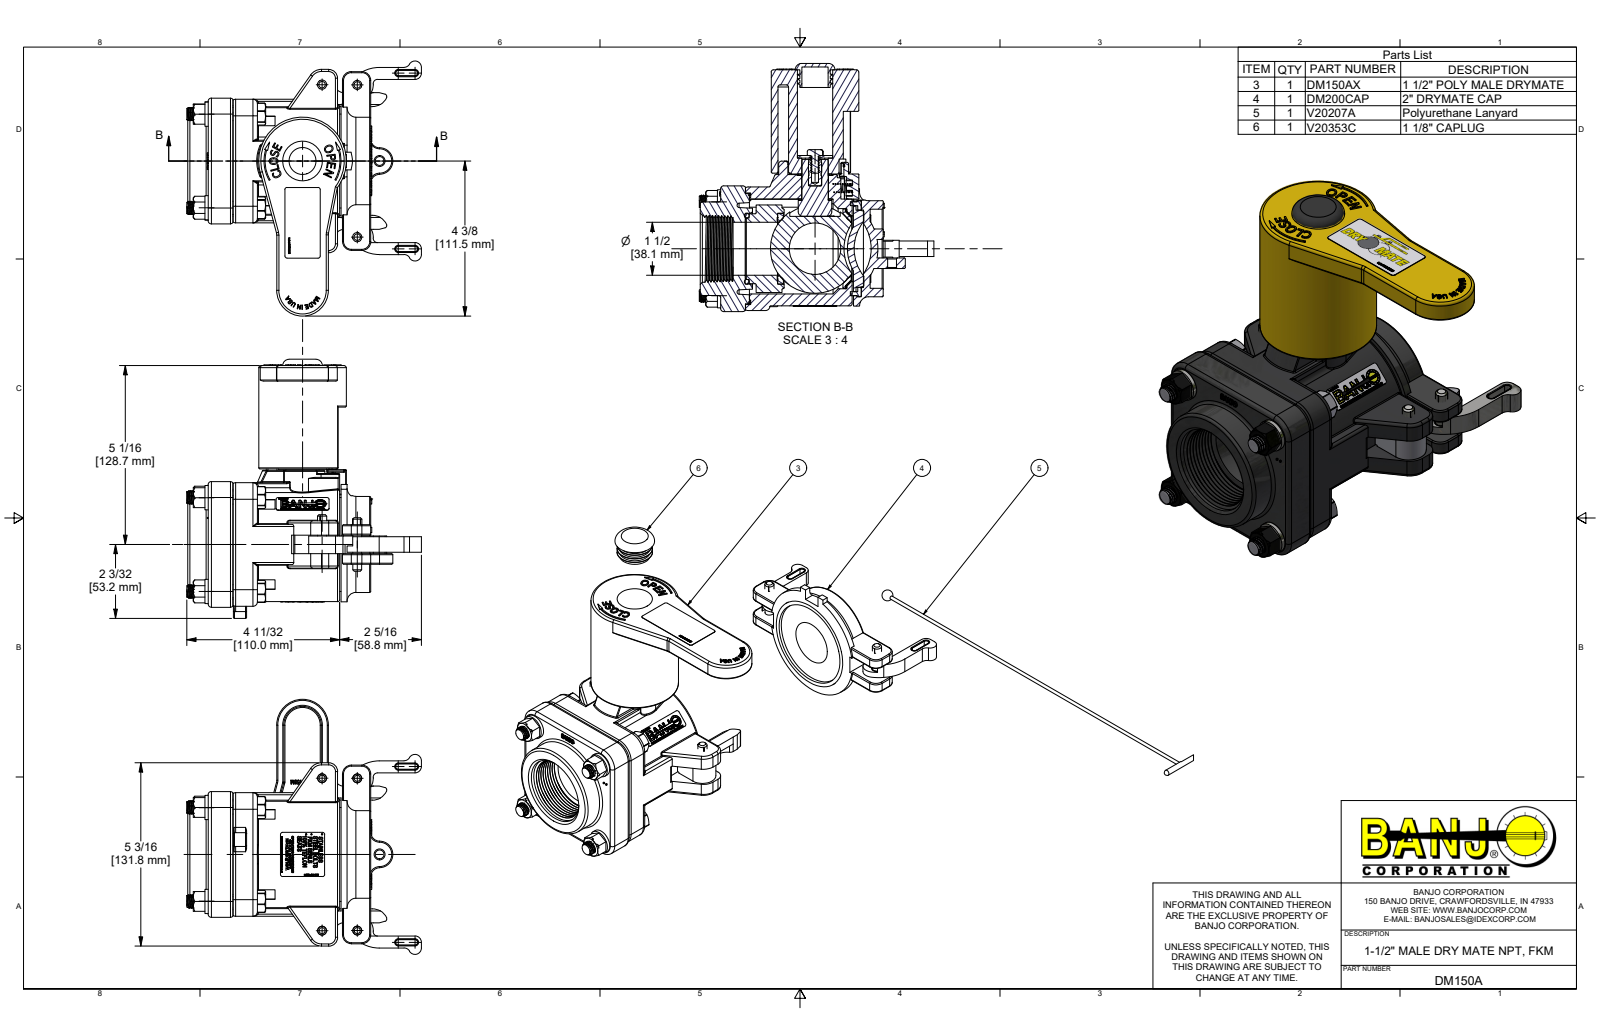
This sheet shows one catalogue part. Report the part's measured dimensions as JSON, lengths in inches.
{"part_name": "DM150A; DM150AX; DM20254; DM20254MY (+8 more)", "step_written_by": "Autodesk Inventor 2022 (AUTOMOTIVE_DESIGN)", "units": "inches", "bodies": {"solids": 45, "faces": 6008, "planar": 2865, "cylindrical": 888, "other": 2255}, "overall_size": [7.34, 7.22, 6.646], "volume_in3": 50.6, "surface_area_in2": 426.8, "round_holes": [[0.25, 5], [0.375, 5], [0.256, 4], [0.307, 4], [0.385, 4], [0.406, 4], [0.42, 4], [0.125, 3], [0.196, 1], [0.2, 1], [0.227, 1], [0.281, 1]], "round_bosses_or_shafts": [[0.324, 60], [0.687, 4], [0.375, 4], [0.26, 4], [0.249, 4], [0.28, 3], [2.48, 2], [3.25, 1]], "partial_cylinders_radius": [[0.03, 104], [0.06, 52], [0.02, 20], [0.01, 12], [0.125, 10], [0.25, 10], [0.09, 8], [0.162, 8]], "face_to_face_distances": [0.298, 3.53, 2.91, 3.725, 0.035, 0.297, 0.25, 0.03, 0.822, 3.28], "hole_center_spacings": [2.653, 1.872, 1.88, 2.648, 2.654, 2.658, 2.659, 3.752]}
